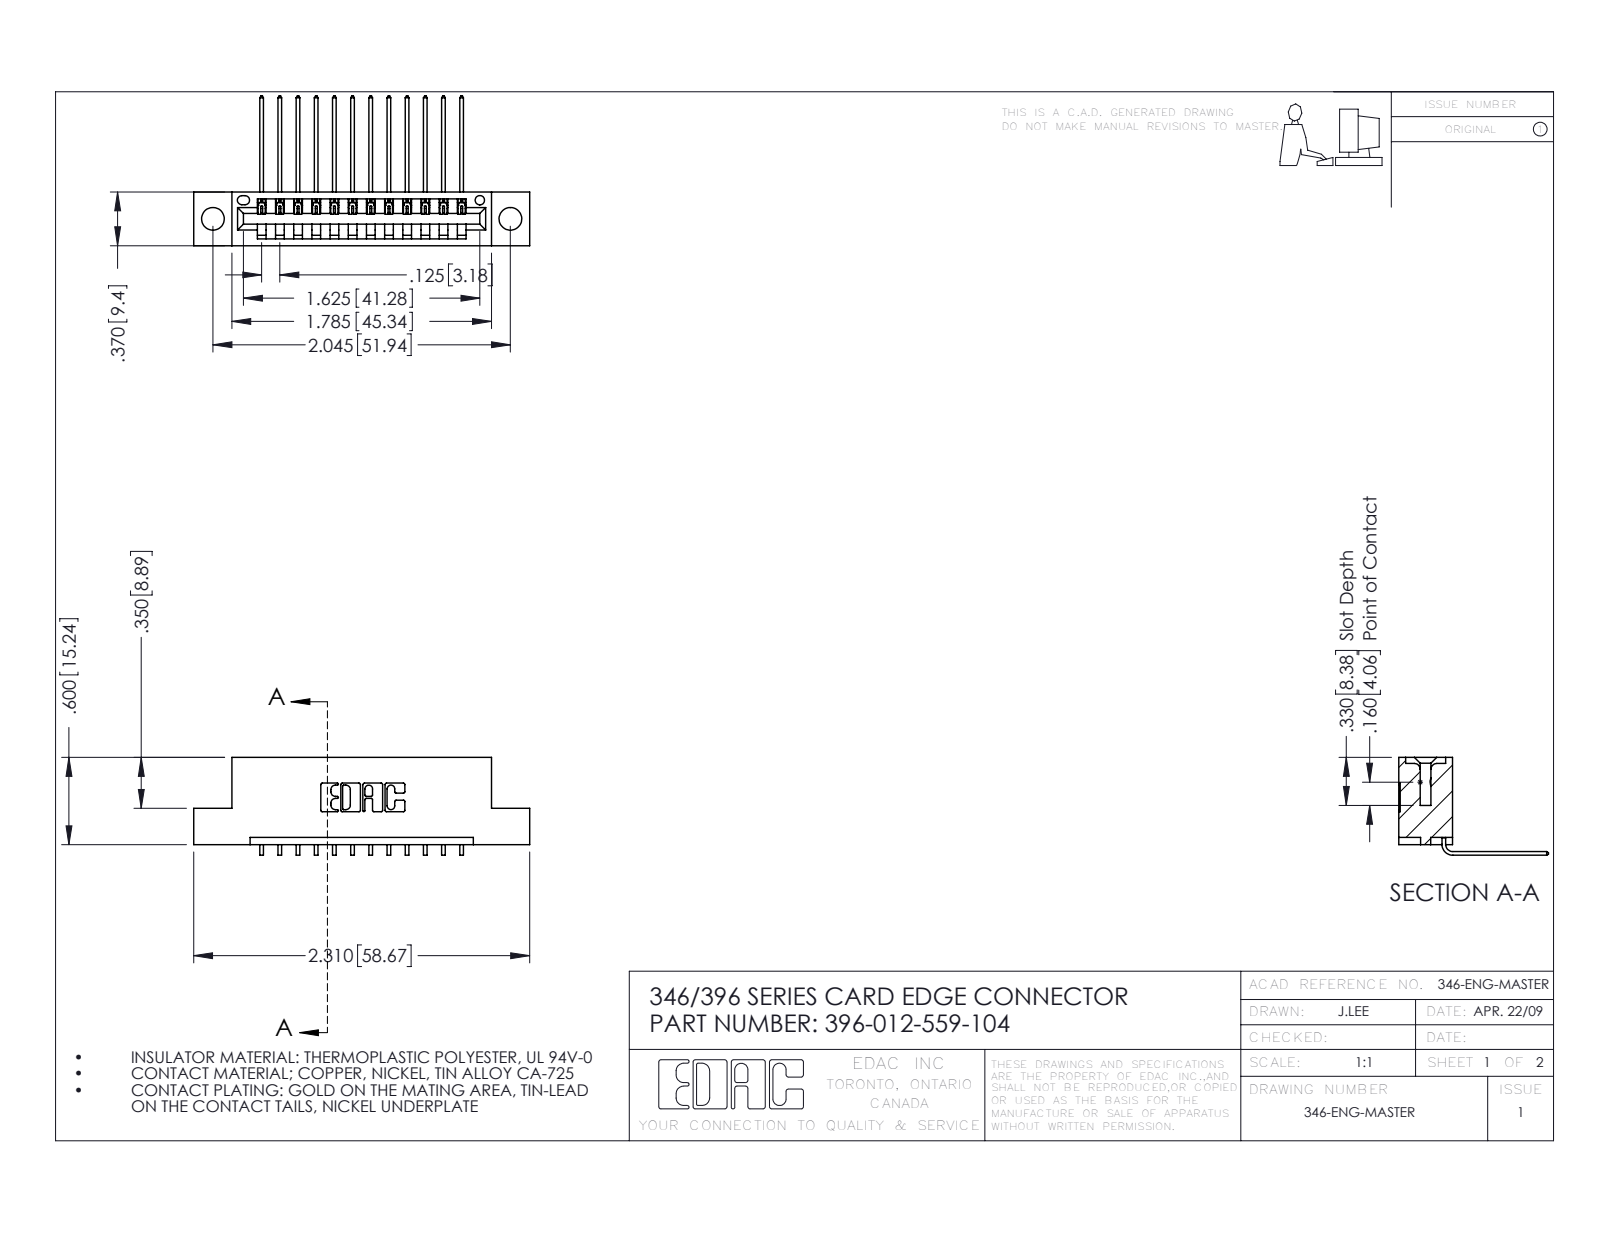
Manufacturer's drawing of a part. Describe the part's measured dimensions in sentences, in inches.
The part is named "346 Part_Flush Mounting Lugs - 0.156 Dia-TH; 345-292-001_558 559 Tail - 1; 396-012-559-104". Its 3-D file was written by "SolidWorks 2016 (CONFIG_CONTROL_DESIGN)". It is 13 solids with 842 faces: 580 planar, 262 cylindrical and 0 other. Overall it measures 2.31 by 1.03 by 0.673 inches. Its volume is 0.327 cubic inches and its surface area 9.953 square inches. Round holes: 2 of diameter 0.156, 1 of diameter 0.064. Partial cylindrical surfaces (rounded edges, fillets, slot ends): 24 of radius 0.006, 22 of radius 0.01, 6 of radius 0.007, 6 of radius 0.031, 3 of radius 0.026, 2 of radius 0.031, 2 of radius 0.04, 1 of radius 0.014. The main face-to-face distances are 0.048, 0.25, 0.322, 0.37, 0.072, 0.025, 0.298, 0.148, 0.222, 0.1. The hole center spacings are 0.246, 1.839, 2.045.
